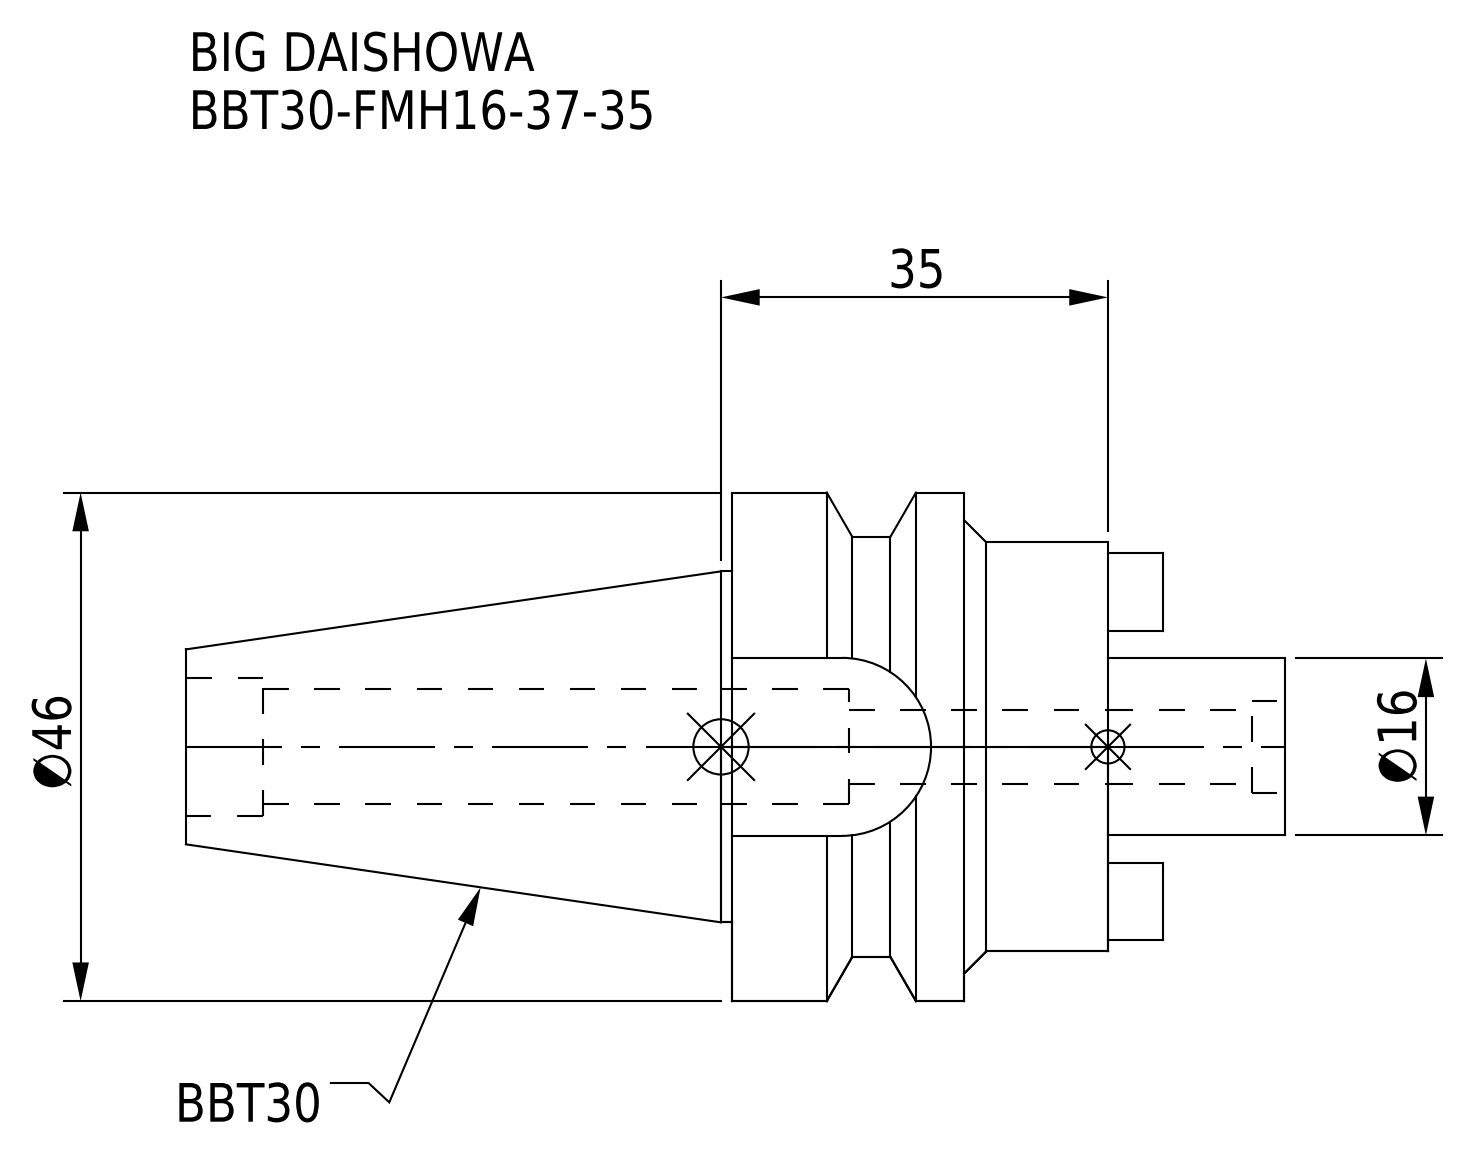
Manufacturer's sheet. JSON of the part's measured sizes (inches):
{"part_name": "BBT30-FMH16-37-35", "step_written_by": "CREO PARAMETRIC BY PTC INC, 2016380 (AUTOMOTIVE_DESIGN)", "units": "inches", "bodies": {"solids": 1, "faces": 58, "planar": 24, "cylindrical": 26, "other": 8}, "overall_size": [3.913, 1.811, 1.811], "volume_in3": 3.966, "surface_area_in2": 24.02, "round_holes": [[0.266, 1], [0.327, 1], [0.409, 1], [0.492, 1]], "round_bosses_or_shafts": [[1.811, 1], [1.457, 1], [1.25, 1], [0.63, 1]], "partial_cylinders_radius": [[0.317, 1], [0.748, 1]], "face_to_face_distances": [1.339, 0.827, 0.512, 1.283, 0.63, 1.142, 1.969, 0.484, 0.799, 3.913]}
